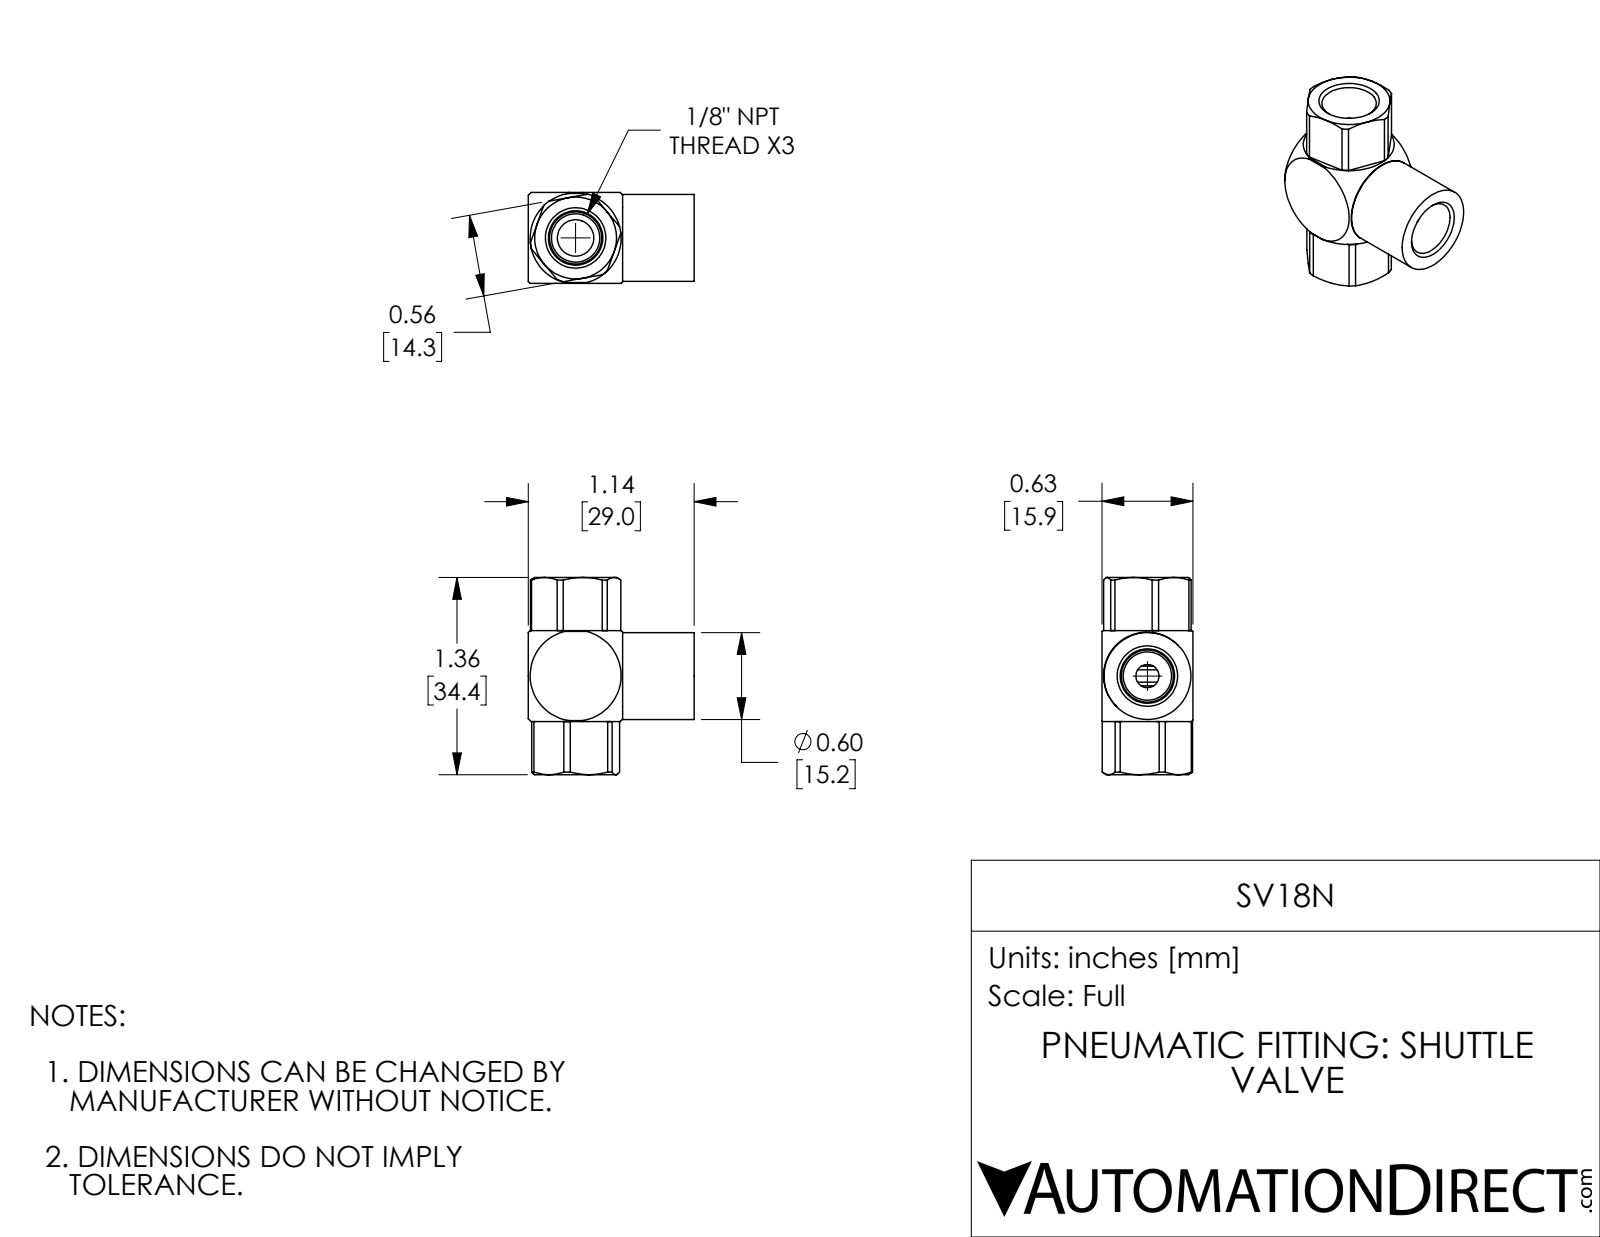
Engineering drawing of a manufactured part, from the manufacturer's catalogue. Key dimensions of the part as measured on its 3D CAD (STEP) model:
Part name (STEP PRODUCT): SV18N
STEP written by: SolidWorks 2018 (AUTOMOTIVE_DESIGN)
Units: inches
Bodies: 3 solids, 111 faces (31 planar, 41 cylindrical, 39 other)
Overall size (bounding box): 1.355 × 1.14 × 0.625
Volume: 0.425 in³ · Surface area: 8.556 in²
Round holes (diameter × count): ⌀0.332 ×2, ⌀0.159 ×1, ⌀0.25 ×1, ⌀0.437 ×1
Round bosses / shafts (diameter × count): ⌀0.597 ×1, ⌀0.495 ×1, ⌀0.439 ×1
Partial cylindrical surfaces — rounded edges, fillets, slot ends (radius × count): R0.313 ×1, R0.437 ×1
Main face-to-face distances: 0.625, 0.562, 0.365, 0.99, 0.635, 0.72, 0.27, 0.355, 0.563, 1.14
